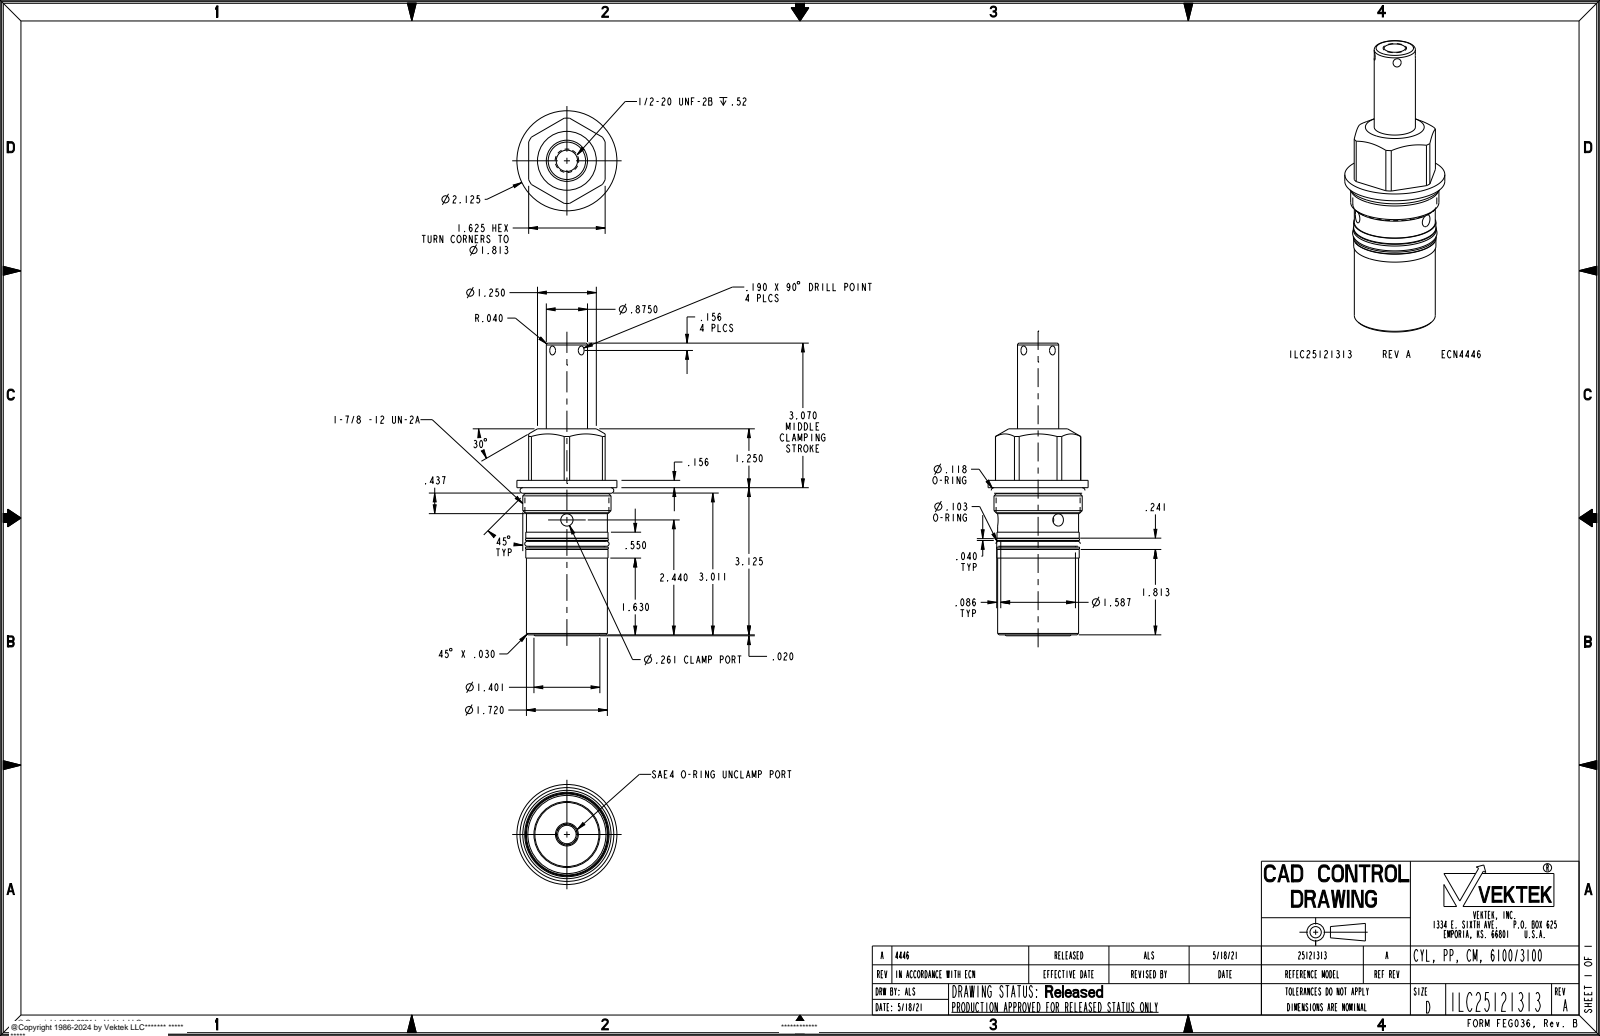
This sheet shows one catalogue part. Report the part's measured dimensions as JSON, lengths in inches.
{"part_name": "ILC25121313", "step_written_by": "PRO/ENGINEER BY PARAMETRIC TECHNOLOGY CORPORATION, 2013320 (CONFIG_CONTROL_DESIGN)", "units": "inches", "bodies": {"solids": 3, "faces": 109, "planar": 27, "cylindrical": 48, "other": 34}, "overall_size": [6.215, 2.125, 2.125], "volume_in3": 11.36, "surface_area_in2": 48.72, "round_holes": [[0.261, 3], [0.392, 1], [0.453, 1]], "round_bosses_or_shafts": [[2.125, 1], [1.875, 1], [1.785, 1], [1.759, 1], [1.756, 1], [1.747, 1], [1.72, 1], [1.587, 1]], "partial_cylinders_radius": [[0.906, 1]], "face_to_face_distances": [1.625, 3.301, 3.145, 0.156, 0.04, 0.18, 0.05, 0.19, 0.23, 1.25]}
